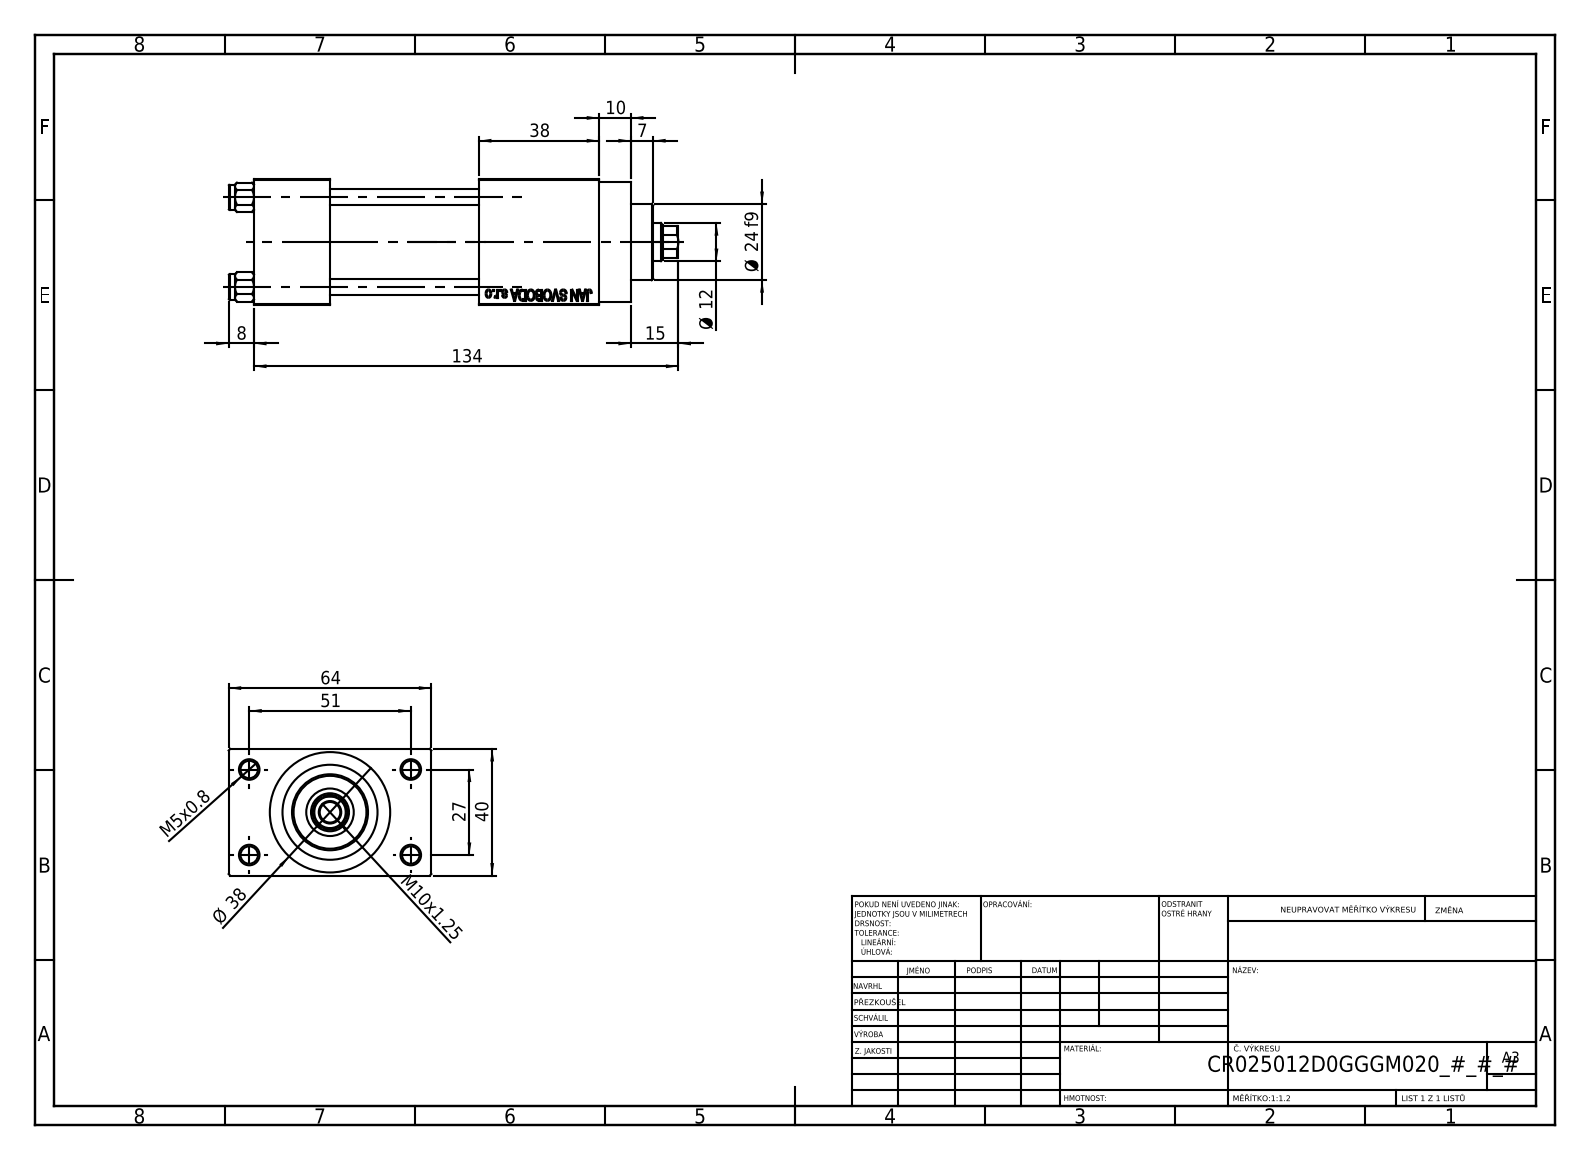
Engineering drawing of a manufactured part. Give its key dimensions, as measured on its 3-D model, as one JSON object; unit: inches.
{"part_name": "V215CR_D_Body; V215CR_VCP_D; V215CR_D_TYCINKA; V215_VC_A (+1 more)", "step_written_by": "SolidWorks 2019 (CONFIG_CONTROL_DESIGN)", "units": "inches", "bodies": {"solids": 11, "faces": 1103, "planar": 496, "cylindrical": 89, "other": 518}, "overall_size": [5.591, 2.52, 1.575], "volume_in3": 10.69, "surface_area_in2": 95.58, "round_holes": [[0.197, 4], [0.217, 4], [0.787, 3], [0.276, 2], [0.518, 2], [0.256, 1], [0.472, 1], [0.591, 1], [0.984, 1], [1.181, 1]], "round_bosses_or_shafts": [[0.315, 4], [1.496, 1], [1.22, 1], [0.945, 1]], "partial_cylinders_radius": [[0.217, 1]], "face_to_face_distances": [1.575, 0.472, 2.047, 1.85, 0.945, 2.795, 2.52, 1.496, 4.291, 3.346], "hole_center_spacings": [0.448, 0.788, 1.114, 1.136, 1.177, 1.561, 1.903, 1.063]}
